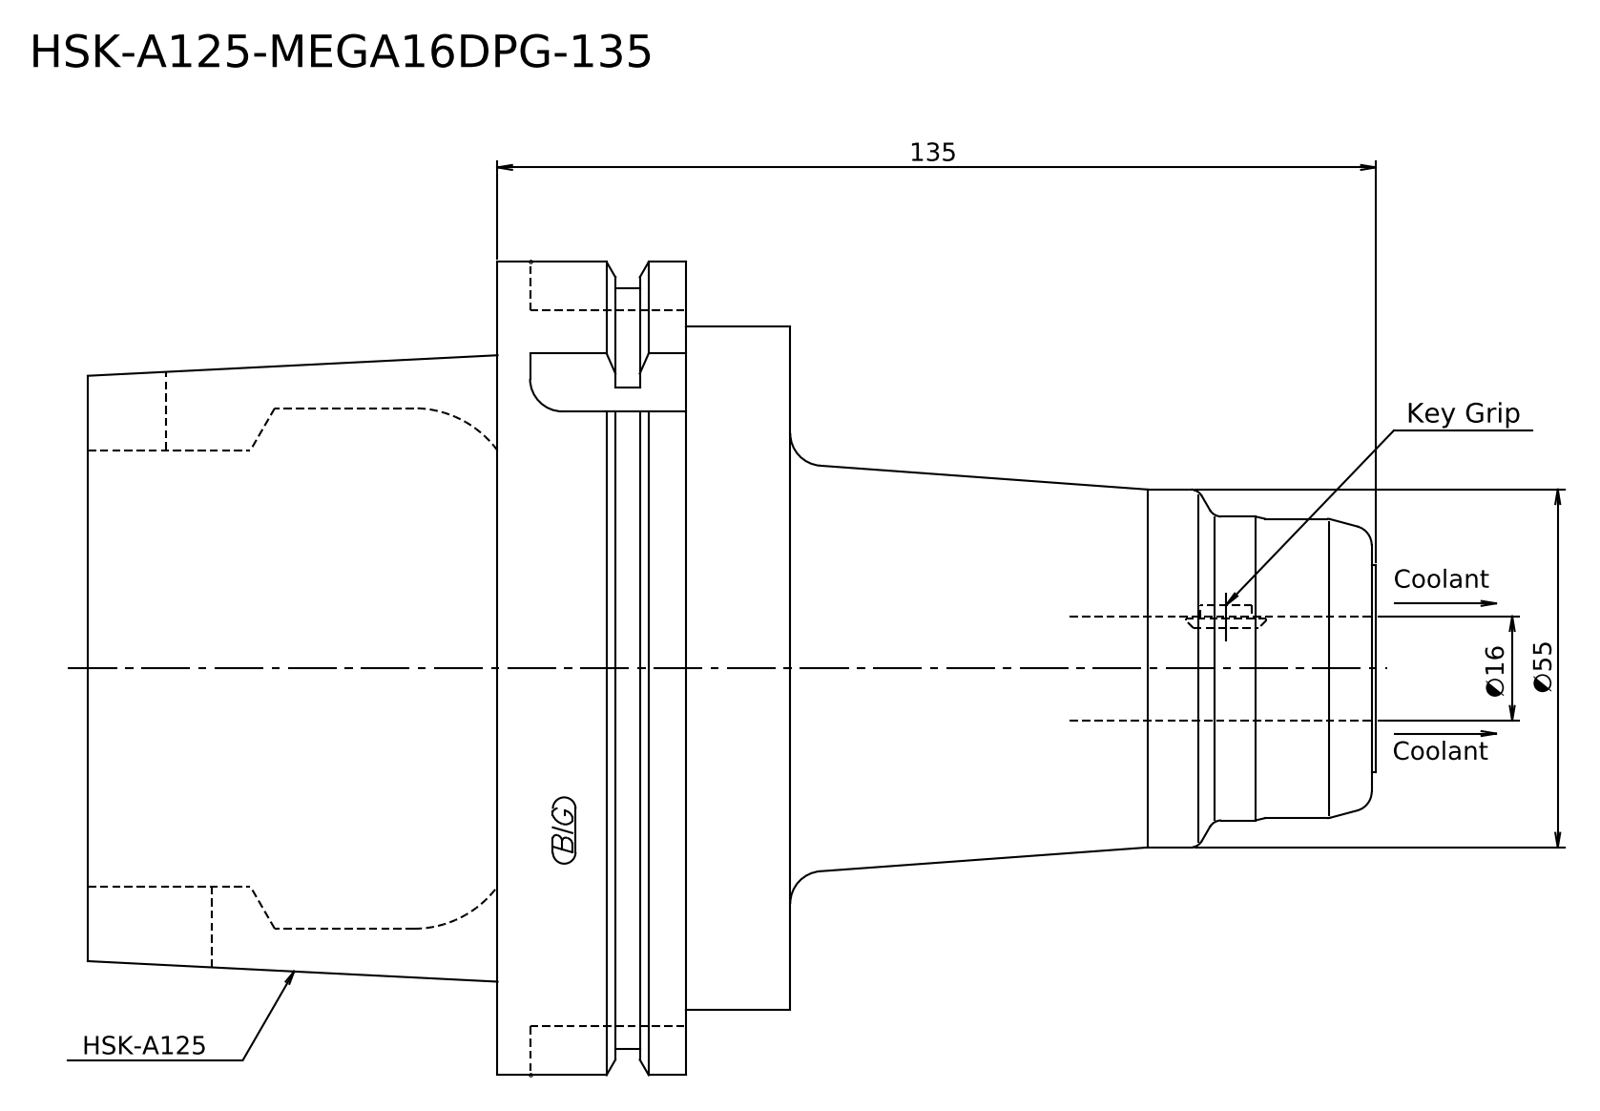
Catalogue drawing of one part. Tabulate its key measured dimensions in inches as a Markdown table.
| quantity | value |
| --- | --- |
| STEP written by | Kubotek KeyCreator 2011 V10.0.2 (22737) (automotive_design) |
| units | inches |
| bodies | 1 solid, 25 faces (8 planar, 8 cylindrical, 9 other) |
| overall size | 7.795 × 4.921 × 4.921 |
| volume | 69.14 in³ |
| surface area | 115.6 in² |
| round bosses / shafts (diameter × count) | 4.921 × 1, 4.606 × 1, 4.134 × 1, 2.165 × 1, 1.839 × 1, 1.811 × 1, 1.25 × 1 |
| main face-to-face distances | 2.48, 1.772, 4.252, 0.63, 1.142, 3.622, 3.543, 4.173, 5.315, 7.795 |
